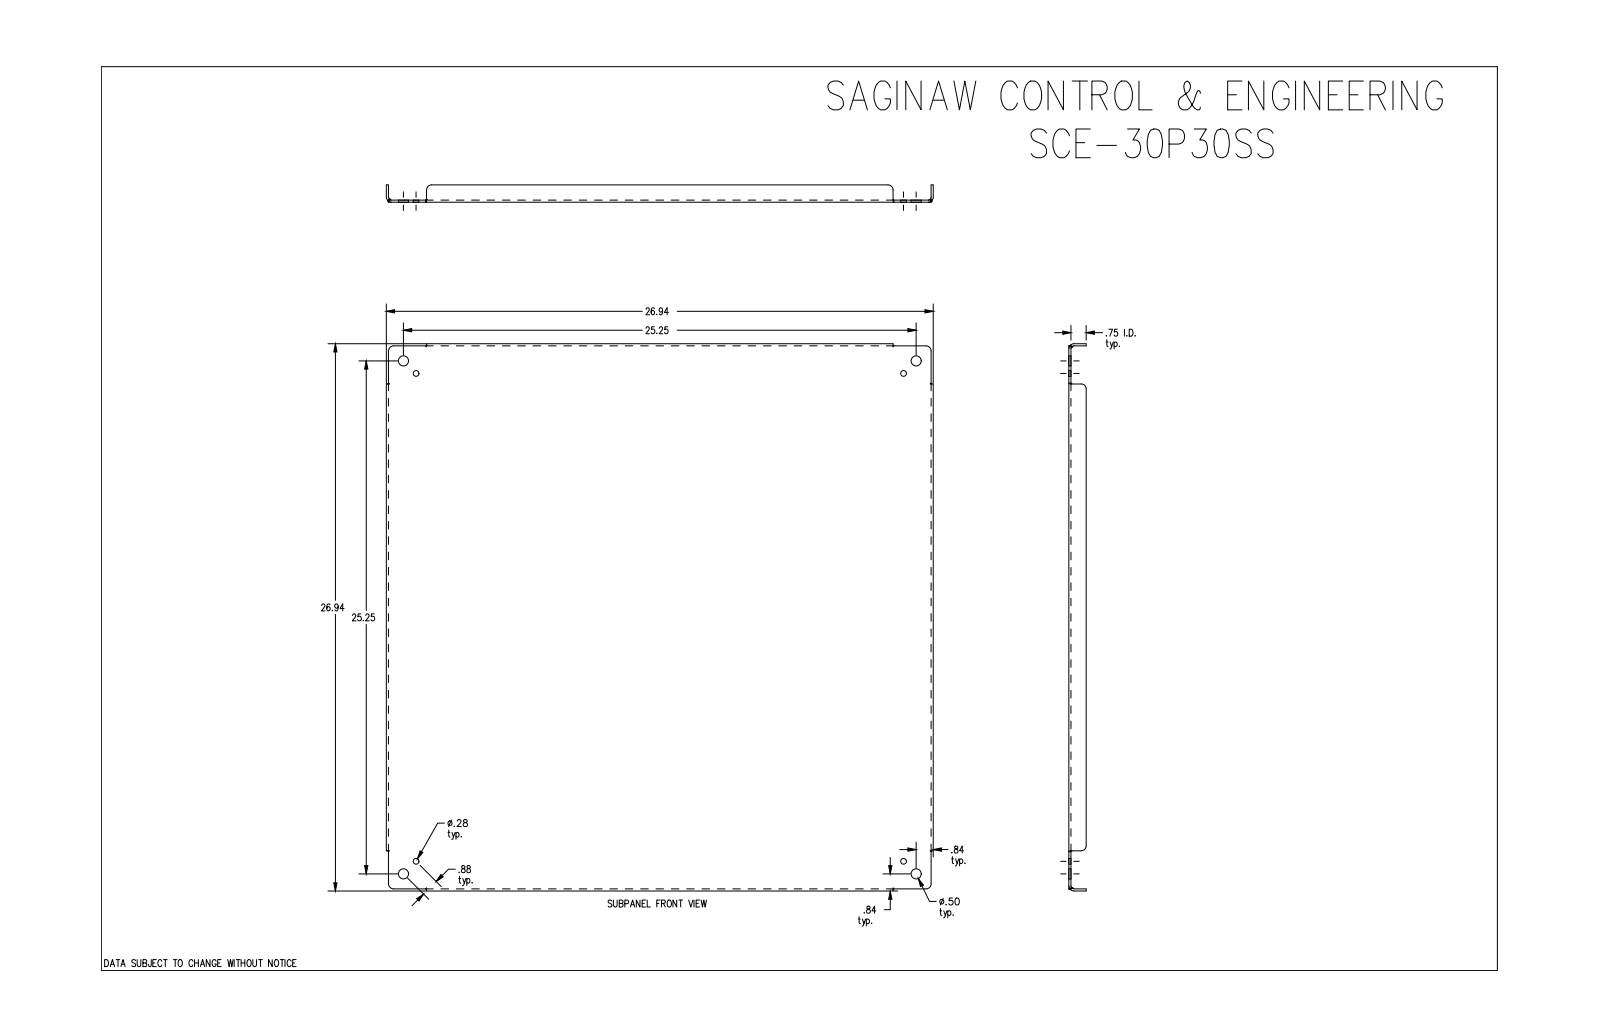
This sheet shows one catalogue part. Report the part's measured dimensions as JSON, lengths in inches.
{"part_name": "SCE-30P30SS", "step_written_by": "SolidWorks 2019 (CONFIG_CONTROL_DESIGN)", "units": "inches", "bodies": {"solids": 1, "faces": 82, "planar": 30, "cylindrical": 28, "other": 24}, "overall_size": [26.938, 26.938, 0.854], "volume_in3": 81.55, "surface_area_in2": 1581, "round_holes": [[0.281, 4], [0.5, 4]], "partial_cylinders_radius": [[0.25, 8], [0.246, 4], [0.142, 2], [0.143, 2]], "face_to_face_distances": [0.104, 26.834, 26.73, 26.938, 0.75, 0.854, 1.979, 24.959, 1.875, 24.855], "hole_center_spacings": [24.64, 0.875, 24.013, 25.25, 34.835, 33.96, 35.709]}
